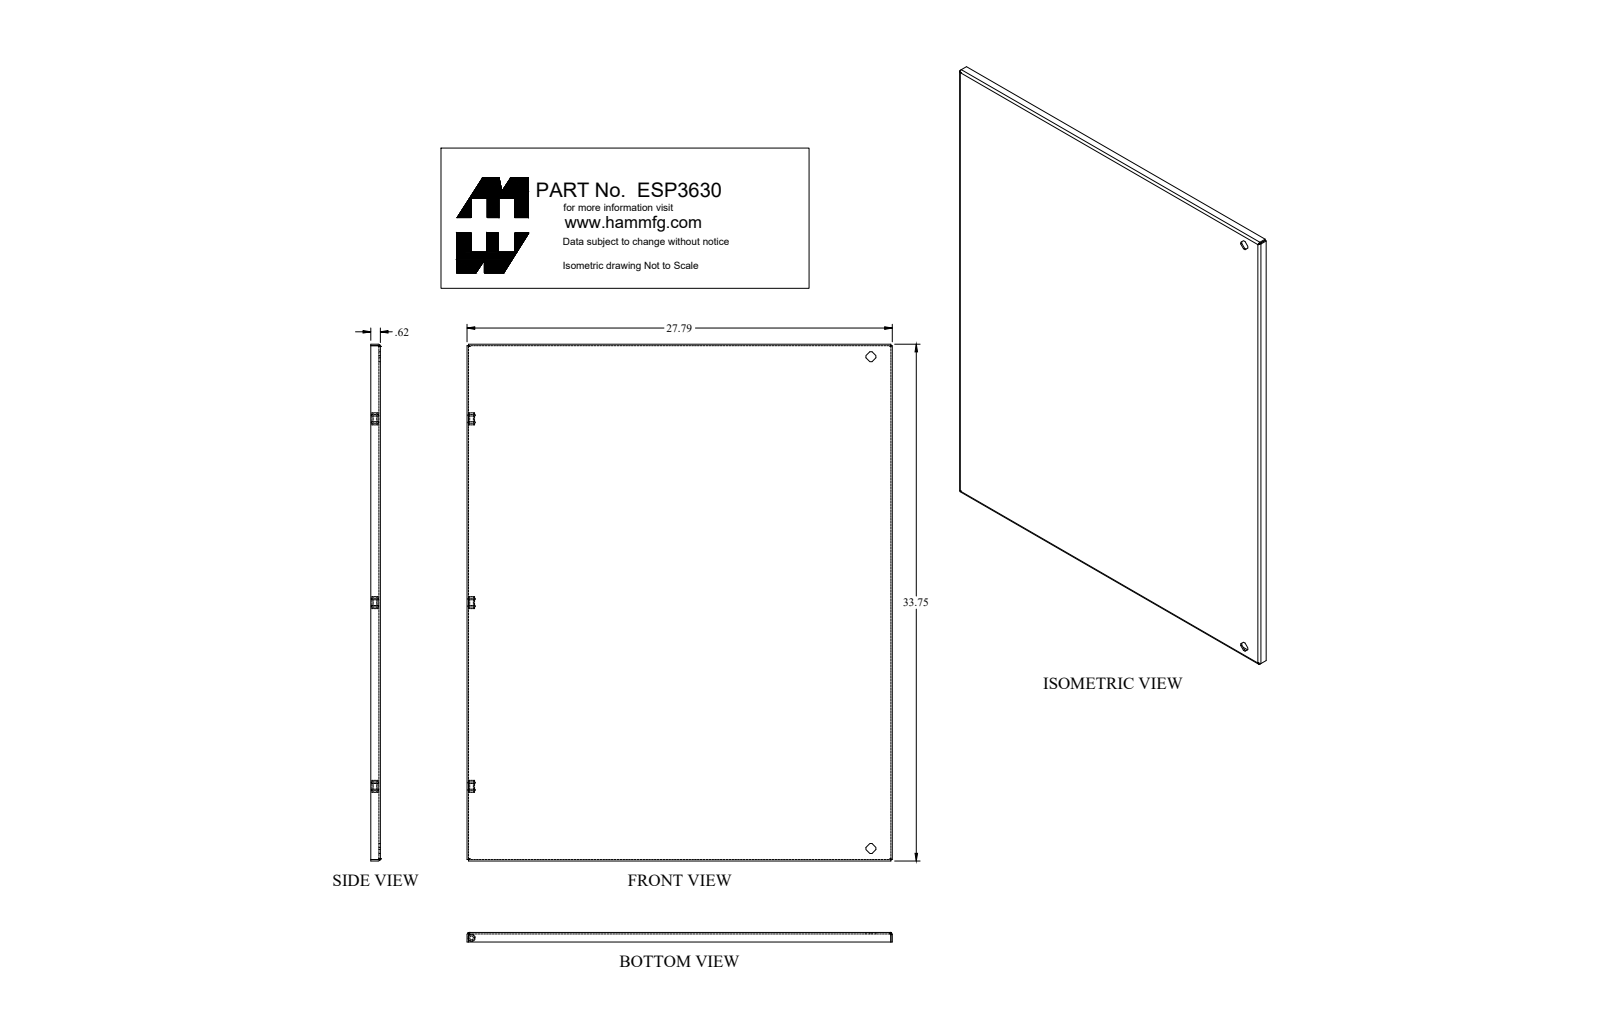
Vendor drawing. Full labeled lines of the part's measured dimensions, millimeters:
Part name (STEP PRODUCT): ESP3630
STEP written by: SolidWorks 2018 (AUTOMOTIVE_DESIGN)
Units: millimetres
Bodies: 14 solids, 634 faces (376 planar, 190 cylindrical, 68 other)
Overall size (bounding box): 857.3 × 754.5 × 252.8
Volume: 1 896 000 mm³ · Surface area: 1 741 000 mm²
Round holes (diameter × count): ⌀3.5 ×3, ⌀6.1 ×3, ⌀13.1 ×2
Round bosses / shafts (diameter × count): ⌀5.9 ×6, ⌀9 ×3, ⌀20 ×2, ⌀13.6 ×2, ⌀12.6 ×2, ⌀11 ×2
Partial cylindrical surfaces — rounded edges, fillets, slot ends (radius × count): R1.2 ×28, R0.3 ×24, R0.9 ×6, R2.7 ×6, R1.5 ×4, R3.6 ×4, R3.9 ×4, R4 ×4
Main face-to-face distances: 2.4, 1.8, 711.4, 1, 713.2, 19.8, 22.2, 21.6, 24.1, 709.6
Hole centre spacings: 330.2, 660.4, 816.8
